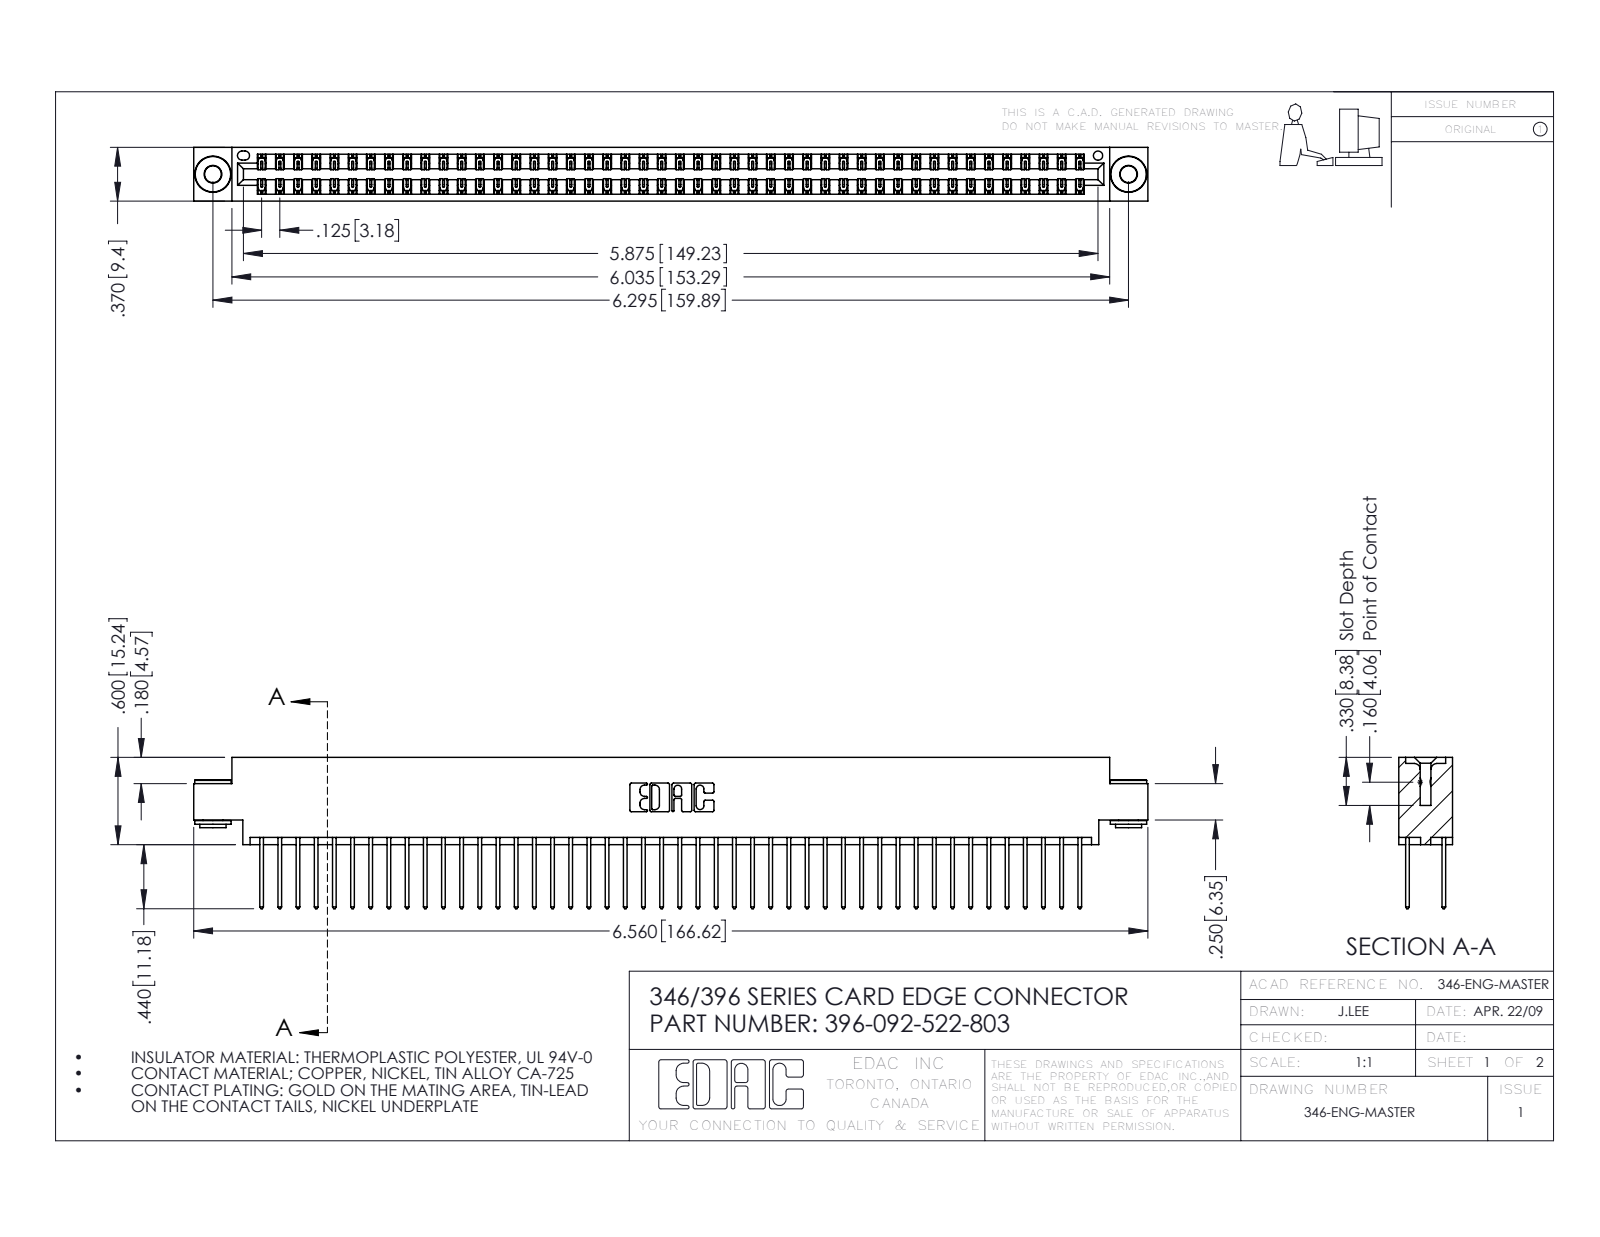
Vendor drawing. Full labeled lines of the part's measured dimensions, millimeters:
Part name (STEP PRODUCT): 345-292-001_345-293-122; 396-092-522-803; 346 Part_0.170 Offset - 0.156 Dia-TH; 345-250-002_345-250-002-102
STEP written by: SolidWorks 2016 (CONFIG_CONTROL_DESIGN)
Units: millimetres
Bodies: 95 solids, 4948 faces (3310 planar, 1630 cylindrical, 8 other)
Overall size (bounding box): 166.6 × 26.4 × 9.4
Volume: 16 390 mm³ · Surface area: 24 060 mm²
Round holes (diameter × count): ⌀2.9 ×2, ⌀4 ×2, ⌀1.6 ×1
Round bosses / shafts (diameter × count): ⌀6.4 ×2, ⌀4.6 ×2, ⌀3.5 ×2
Partial cylindrical surfaces — rounded edges, fillets, slot ends (radius × count): R0.2 ×138, R0.3 ×92, R0.3 ×22, R0.2 ×6, R0.8 ×6, R0.7 ×3, R0.4 ×2, R0.6 ×2
Main face-to-face distances: 1.2, 8.2, 6.4, 9.4, 0.6, 1.8, 7.6, 7, 3.8, 5.6
Hole centre spacings: 6.2, 154.6, 159.9
